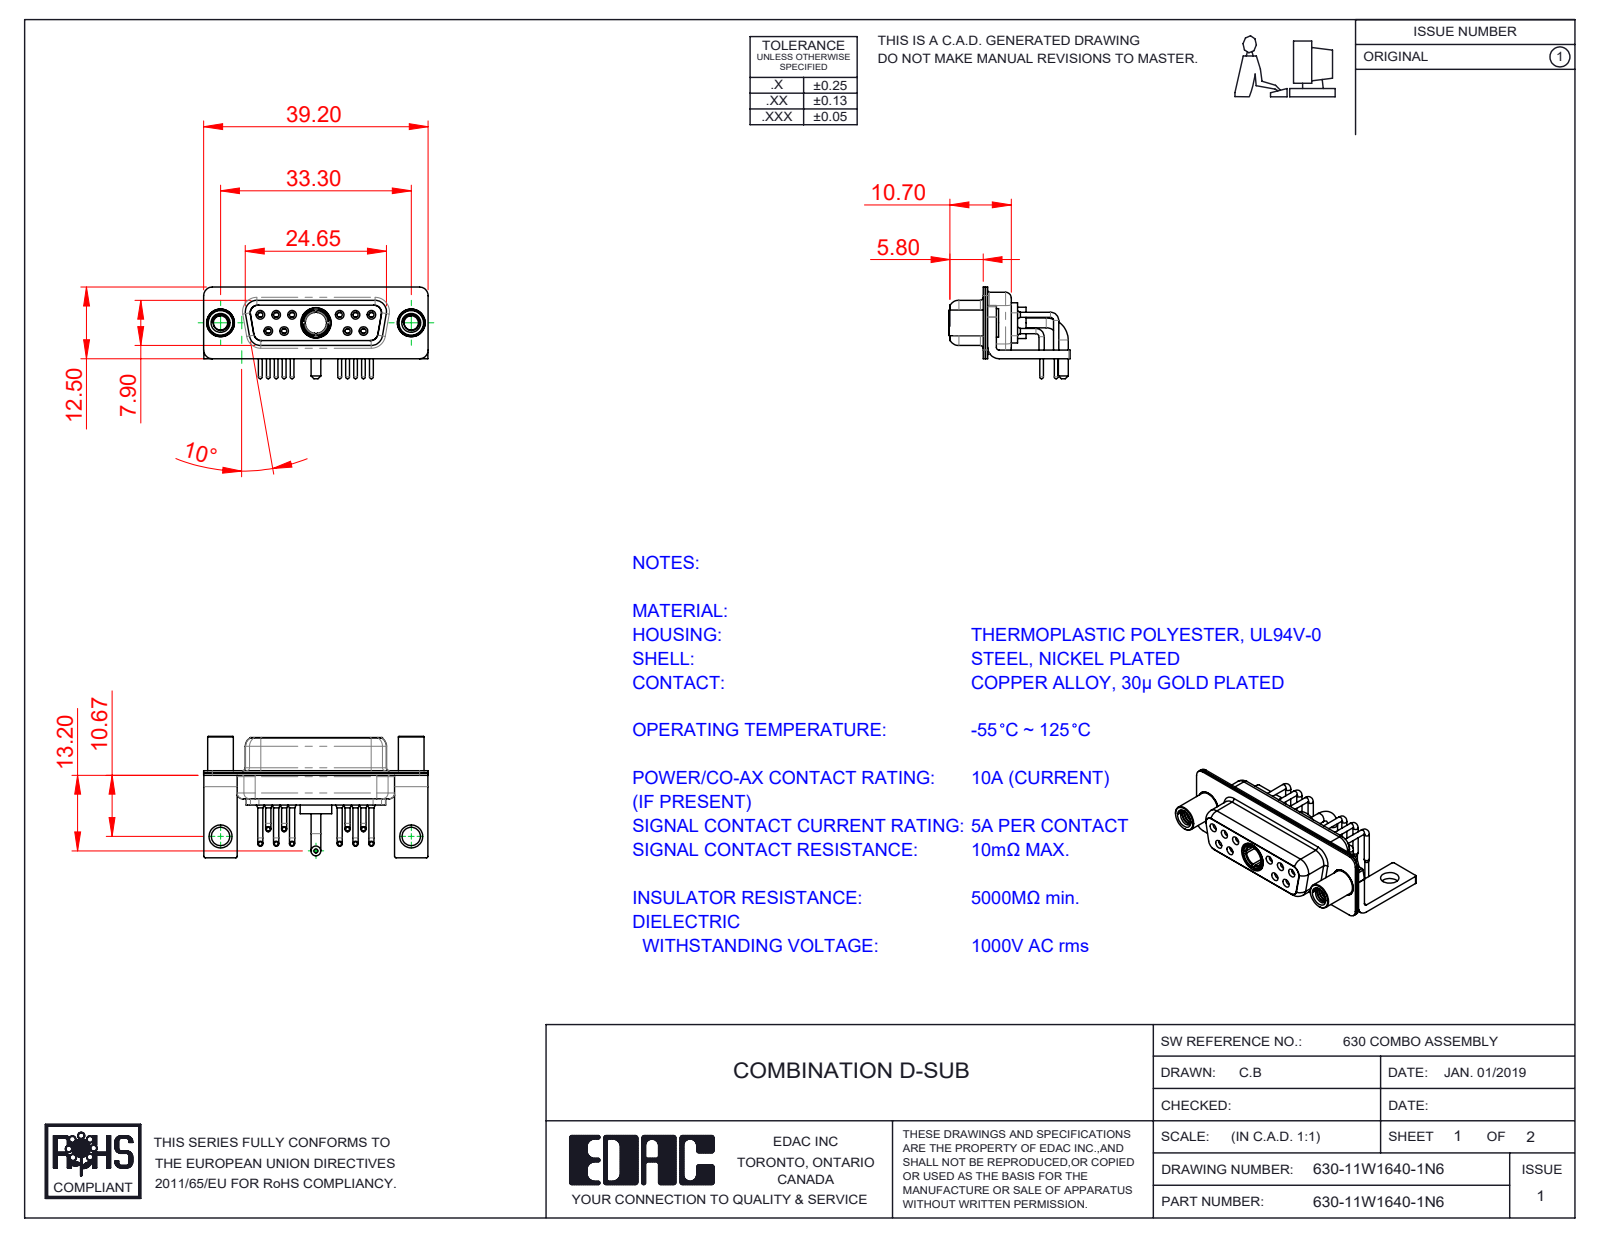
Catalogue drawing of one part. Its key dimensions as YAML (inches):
part_name: "630Combo Contact Row 1; 630Combo Housing_11W1; 630Combo Stabilizer Bracket; 630Combo Shell Front_15 Contacts (+5 more)"
step_written_by: "SolidWorks 2020 (CONFIG_CONTROL_DESIGN)"
units: inches
bodies: {solids: 19, faces: 985, planar: 268, cylindrical: 464, other: 253}
overall_size: [1.543, 0.835, 0.63]
volume: 0.181
surface_area: 11.08
round_holes:
  - {diameter: 0.035, count: 10}
  - {diameter: 0.043, count: 10}
  - {diameter: 0.059, count: 10}
  - {diameter: 0.079, count: 10}
  - {diameter: 0.067, count: 6}
  - {diameter: 0.063, count: 4}
  - {diameter: 0.191, count: 3}
  - {diameter: 0.098, count: 2}
  - {diameter: 0.126, count: 2}
  - {diameter: 0.157, count: 2}
  - {diameter: 0.159, count: 2}
  - {diameter: 0.146, count: 1}
round_bosses_or_shafts:
  - {diameter: 0.035, count: 10}
  - {diameter: 0.026, count: 10}
  - {diameter: 0.063, count: 6}
  - {diameter: 0.197, count: 2}
  - {diameter: 0.195, count: 2}
  - {diameter: 0.189, count: 2}
  - {diameter: 0.177, count: 2}
  - {diameter: 0.067, count: 2}
partial_cylinders:
  - {radius: 0.01, count: 16}
  - {radius: 0.059, count: 16}
  - {radius: 0.079, count: 13}
  - {radius: 0.053, count: 12}
  - {radius: 0.063, count: 8}
  - {radius: 0.02, count: 5}
  - {radius: 0.024, count: 4}
  - {radius: 0.026, count: 4}
face_to_face_distances: [0.016, 0.031, 0.055, 0.018, 0.333, 0.059, 0.071, 0.35, 0.244, 0.091]
hole_center_spacings: [0.124, 0.109, 0.545, 0.436, 0.654, 0.198, 0.198, 0.218]
